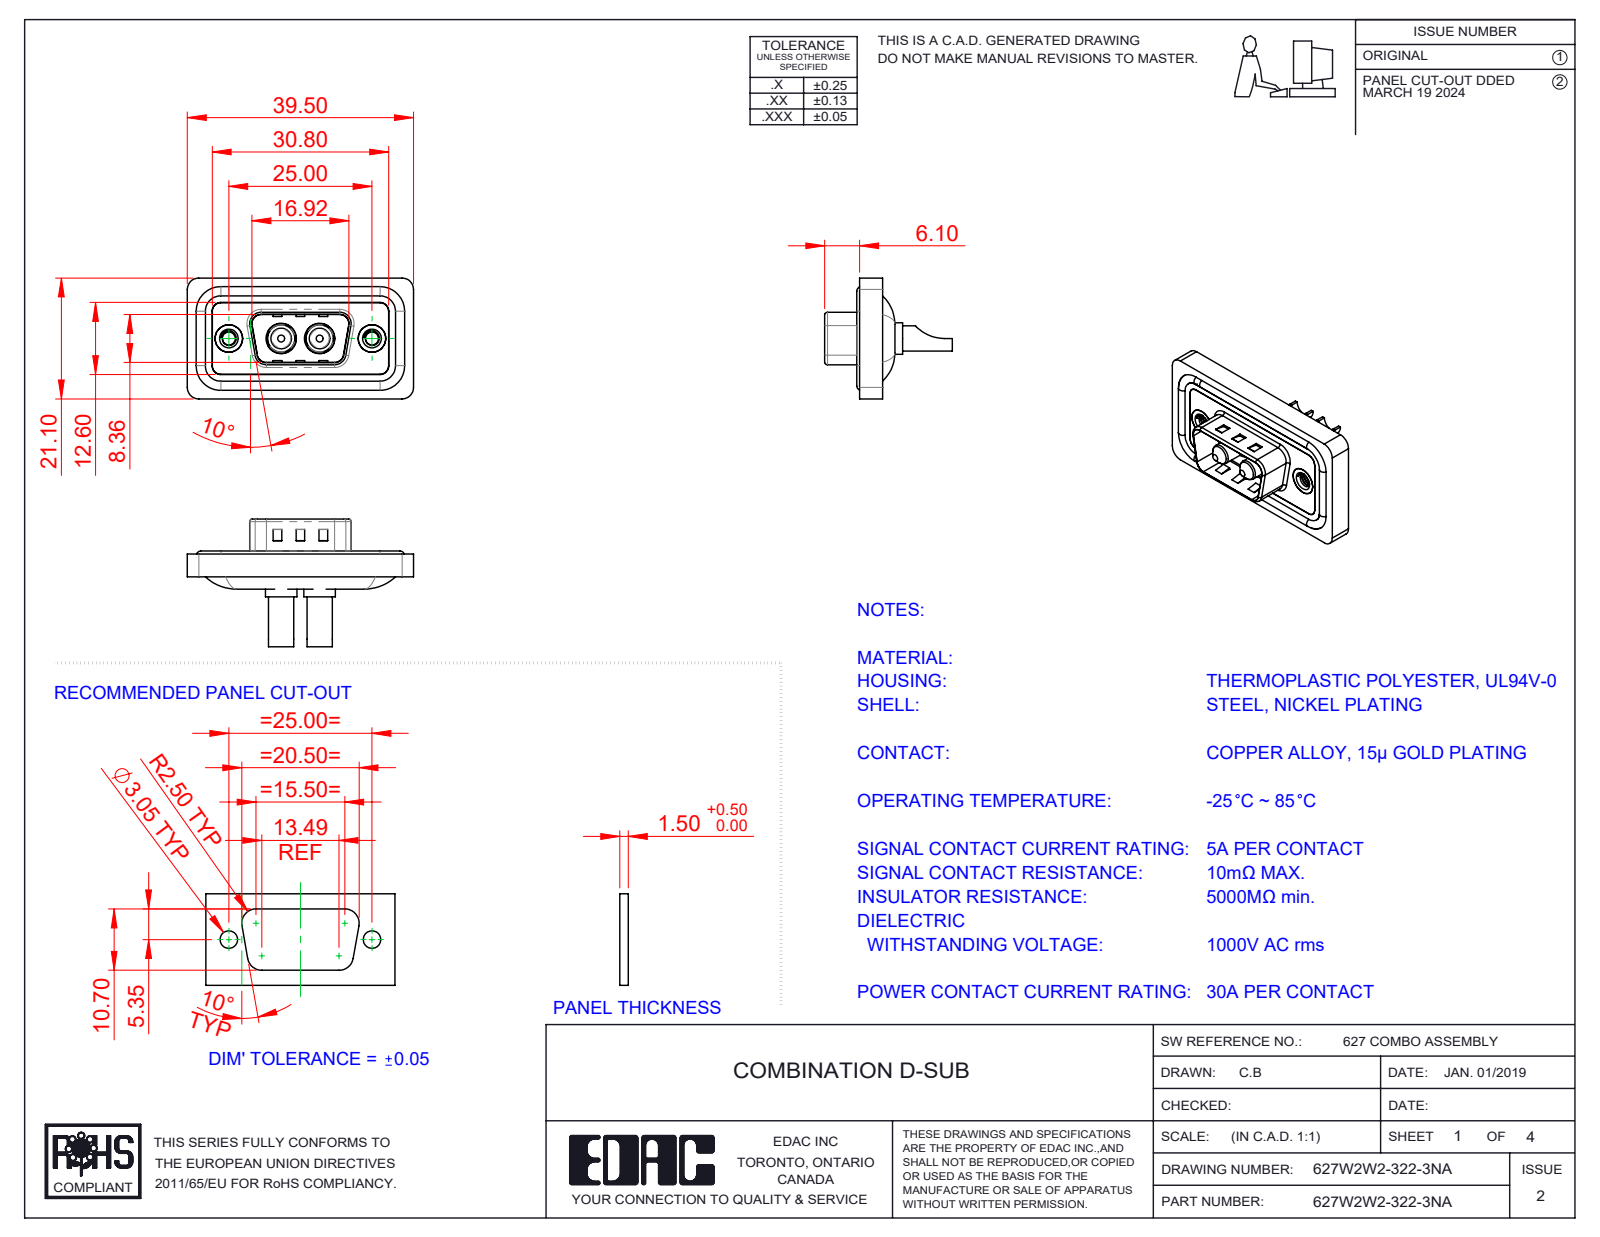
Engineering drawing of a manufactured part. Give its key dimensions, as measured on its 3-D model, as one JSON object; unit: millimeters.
{"part_name": "627Combo Shell Rear_09 Contacts; 627Combo Threaded Rivet_A; 627Combo Shell Front_09 Contacts; Power Pin_30A SC (+3 more)", "step_written_by": "SolidWorks 2023 (CONFIG_CONTROL_DESIGN)", "units": "millimeters", "bodies": {"solids": 11, "faces": 499, "planar": 171, "cylindrical": 226, "other": 102}, "overall_size": [39.5, 22.3, 21.1], "volume_mm3": 4510, "surface_area_mm2": 7197, "round_holes": [[2.26, 2], [3.5, 2], [4, 2], [4.8, 2], [4.85, 2], [5, 2], [5.3, 2]], "round_bosses_or_shafts": [[1.6, 4], [5.5, 2], [5.2, 2], [4.9, 2], [4.75, 2], [4.4, 2], [3.75, 2], [3.6, 2]], "partial_cylinders_radius": [[1.5, 22], [2, 18], [0.5, 8], [1.6, 8], [0.25, 4], [0.6, 4], [0.65, 4], [0.9, 4]], "face_to_face_distances": [0.4, 1.1, 2.9, 3.1, 0.5, 1.6, 1.5, 2.5, 4, 0.7], "hole_center_spacings": [9.14, 15.86, 6.72, 25]}
